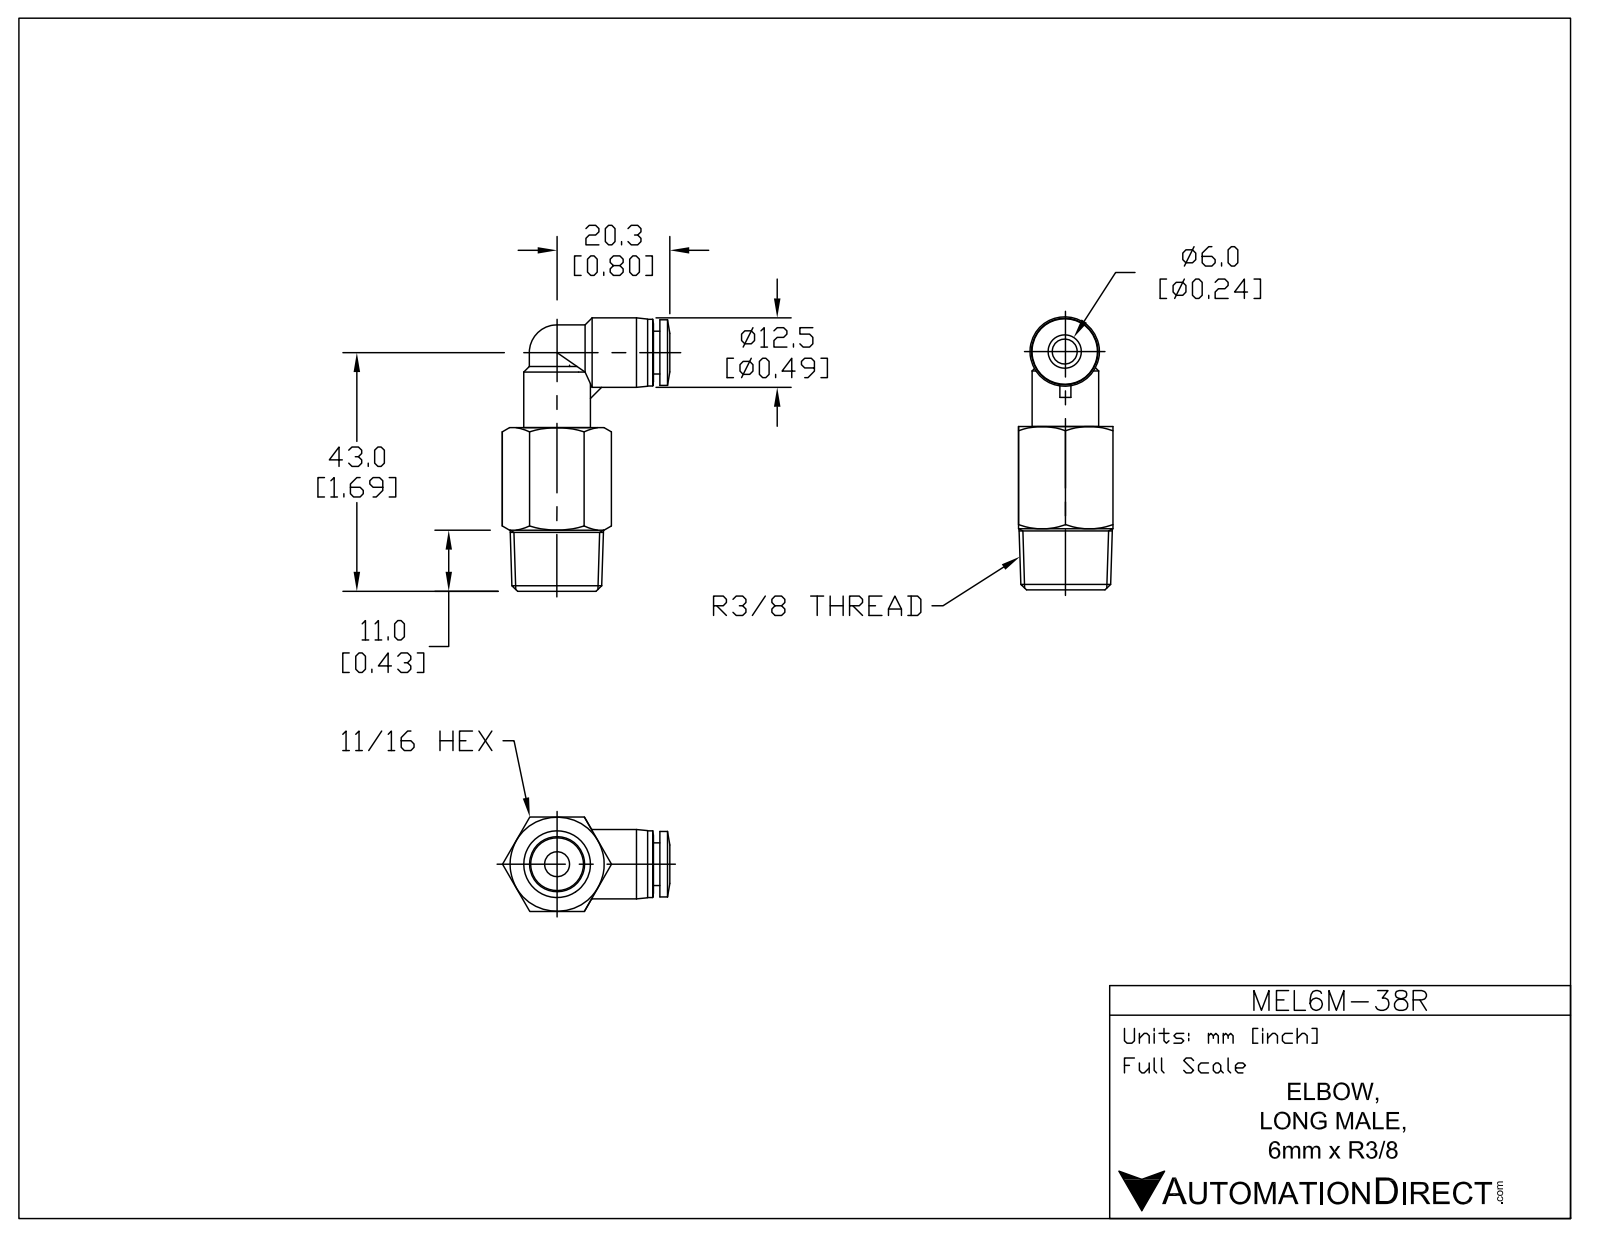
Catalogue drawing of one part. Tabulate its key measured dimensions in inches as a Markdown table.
| quantity | value |
| --- | --- |
| part name | MEL6M-38R |
| STEP written by | SolidWorks 2015 (AUTOMOTIVE_DESIGN) |
| units | inches |
| bodies | 1 solid, 69 faces (17 planar, 19 cylindrical, 33 other) |
| overall size | 1.939 × 1.186 × 0.669 |
| volume | 0.568 in³ |
| surface area | 6.651 in² |
| round holes (diameter × count) | 0.157 × 2, 0.248 × 1 |
| round bosses / shafts (diameter × count) | 0.472 × 2, 0.492 × 1, 0.465 × 1, 0.303 × 1 |
| partial cylindrical surfaces (radius × count) | 0.197 × 2 |
| main face-to-face distances | 0.669, 1.161, 0.045, 0.53, 0.575, 0.433, 0.728, 0.295, 0.374, 0.646 |
